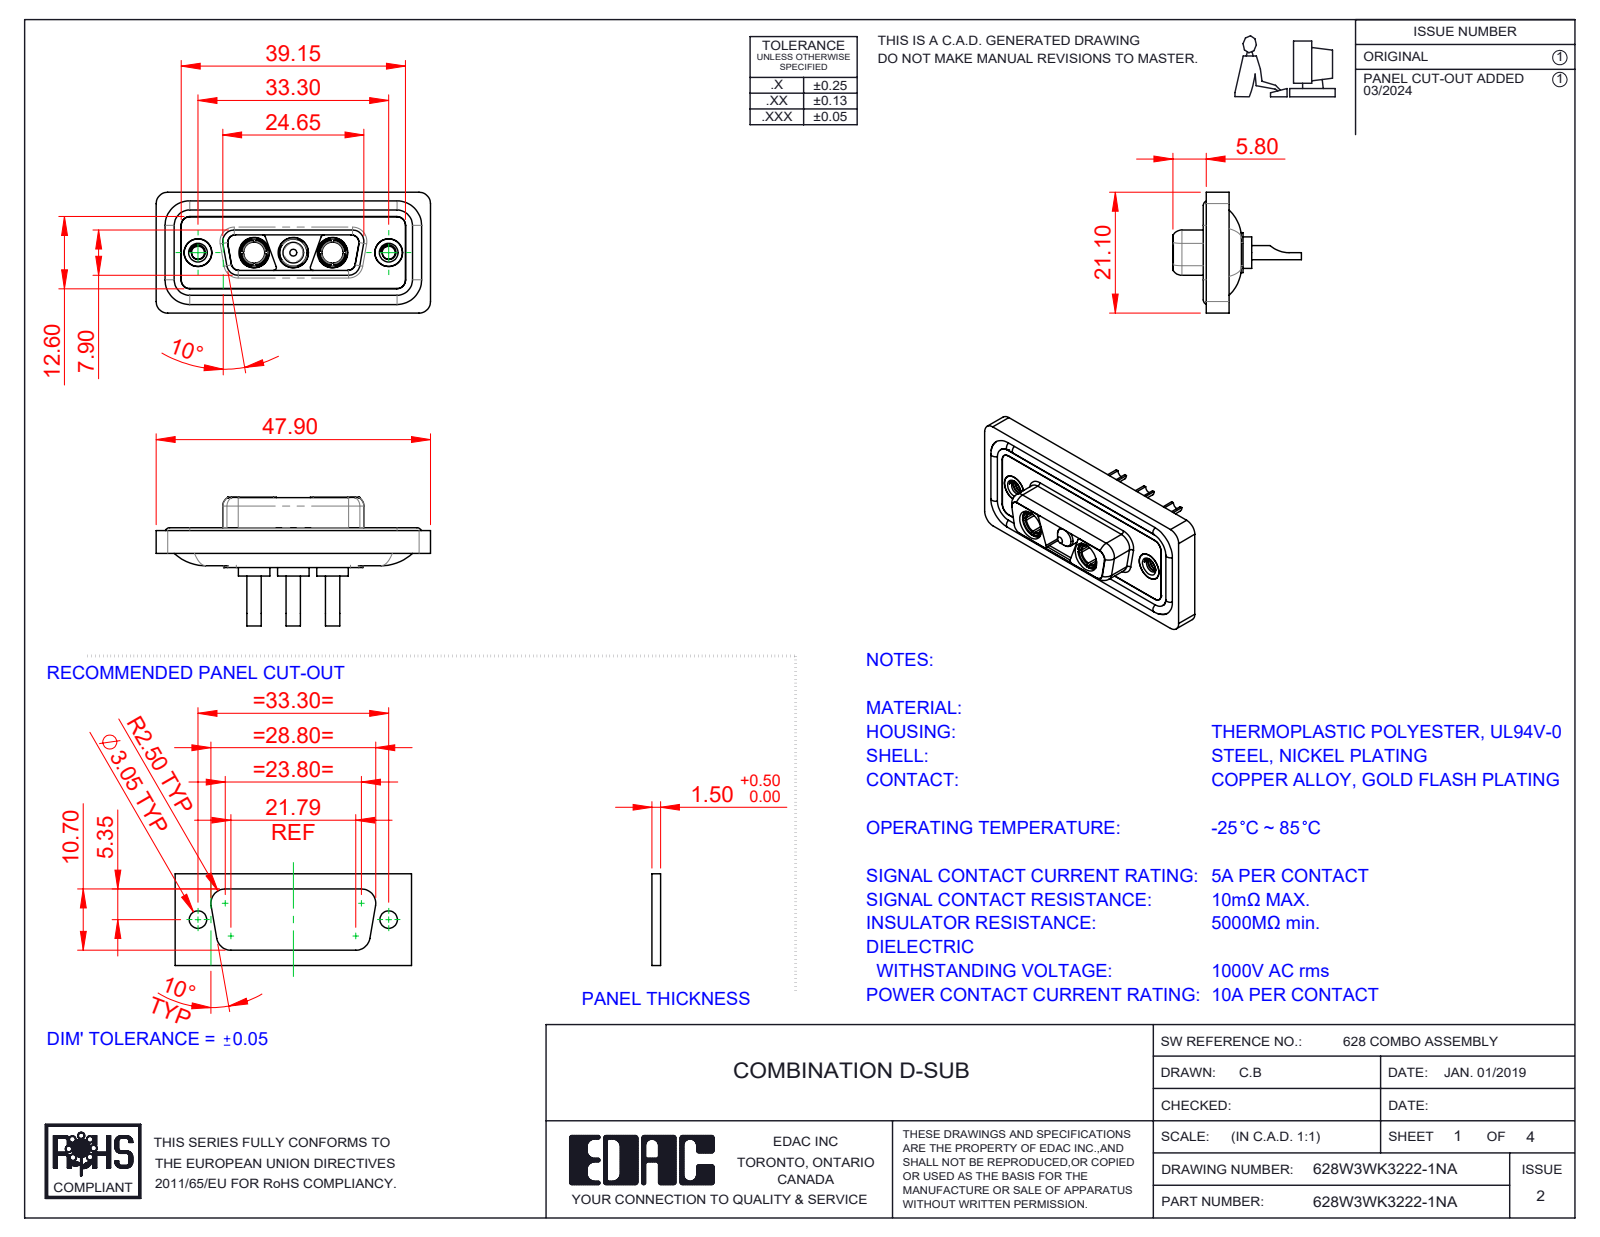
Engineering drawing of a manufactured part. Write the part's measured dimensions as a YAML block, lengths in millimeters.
part_name: "628Combo Housing_3WK3; 628Combo Shell Front_15 Contacts; 628Combo Threaded Rivet_A; Power Socket_10A SC (+4 more)"
step_written_by: "SolidWorks 2023 (CONFIG_CONTROL_DESIGN)"
units: millimeters
bodies: {solids: 13, faces: 597, planar: 184, cylindrical: 269, other: 144}
overall_size: [47.9, 22.45, 21.1]
volume: 5871
surface_area: 9645
round_holes:
  - {diameter: 4.85, count: 5}
  - {diameter: 1.7, count: 3}
  - {diameter: 5.3, count: 3}
  - {diameter: 2.26, count: 2}
  - {diameter: 3.7, count: 2}
  - {diameter: 4, count: 2}
  - {diameter: 4.05, count: 2}
  - {diameter: 5, count: 2}
round_bosses_or_shafts:
  - {diameter: 1.6, count: 4}
  - {diameter: 5.5, count: 3}
  - {diameter: 5.2, count: 3}
  - {diameter: 4.75, count: 3}
  - {diameter: 3.75, count: 3}
  - {diameter: 2.5, count: 3}
  - {diameter: 4.96, count: 2}
  - {diameter: 4.95, count: 2}
partial_cylinders:
  - {radius: 1.5, count: 22}
  - {radius: 2, count: 20}
  - {radius: 1.35, count: 12}
  - {radius: 0.5, count: 8}
  - {radius: 1.6, count: 8}
  - {radius: 0.25, count: 4}
  - {radius: 0.6, count: 4}
  - {radius: 0.65, count: 4}
face_to_face_distances: [0.4, 1.6, 1.8, 0.5, 1.1, 2.9, 5.65, 7.05, 1.5, 5.35]
hole_center_spacings: [6.85, 9.8, 16.65, 23.5, 13.7, 33.3]
